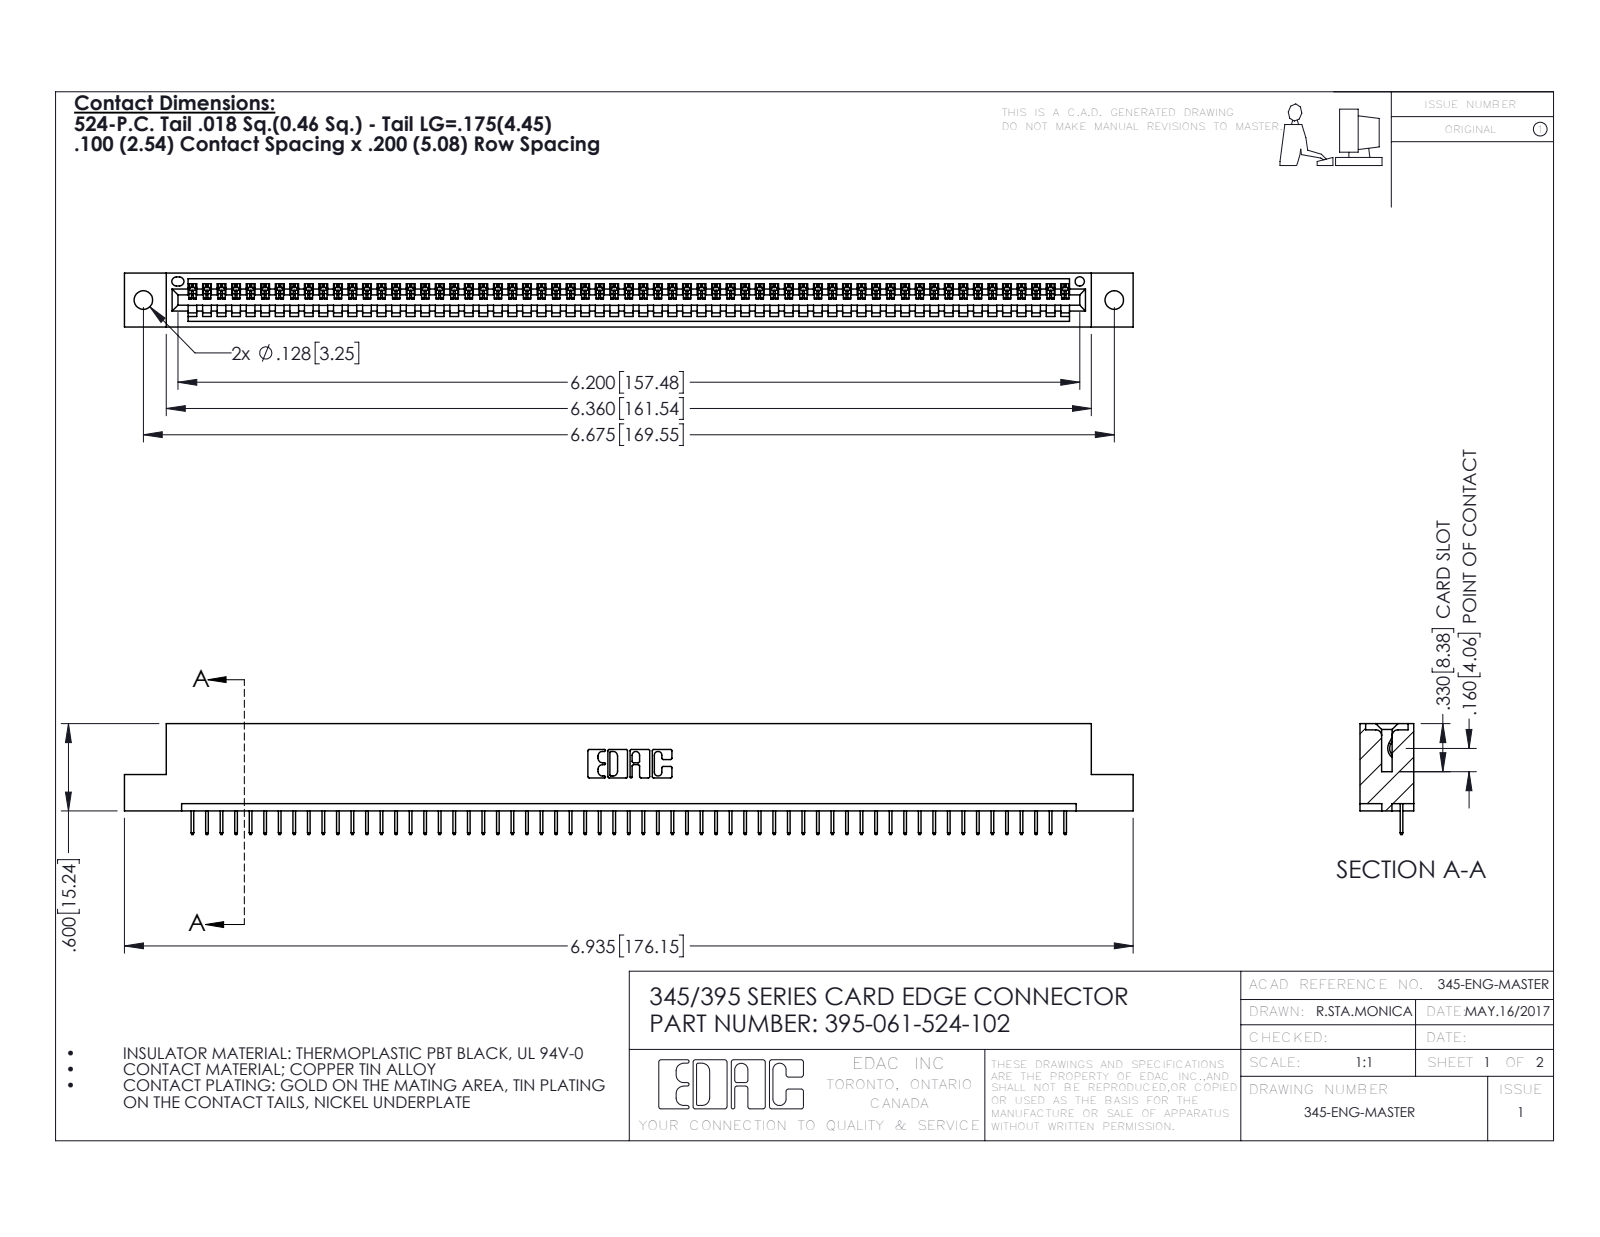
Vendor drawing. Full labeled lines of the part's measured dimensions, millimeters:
Part name (STEP PRODUCT): 345 Part_Flush Mounting Lugs - 0.128 Dia; 345-292-001_345-293-124; 395-061-524-102
STEP written by: SolidWorks 2016 (CONFIG_CONTROL_DESIGN)
Units: millimetres
Bodies: 62 solids, 3908 faces (2886 planar, 1022 cylindrical, 0 other)
Overall size (bounding box): 176.1 × 19.4 × 9.4
Volume: 16 620 mm³ · Surface area: 21 290 mm²
Round holes (diameter × count): ⌀3.3 ×2, ⌀1.6 ×1
Partial cylindrical surfaces — rounded edges, fillets, slot ends (radius × count): R0.2 ×122, R0.3 ×22, R0.2 ×6, R0.8 ×6, R0.7 ×3, R0.8 ×2, R1 ×2, R0.4 ×1
Main face-to-face distances: 7.6, 1.8, 9.4, 5.1, 2.5, 6.9, 0.6, 5.7, 1.8, 3.8
Hole centre spacings: 6.9, 163.6, 169.5
